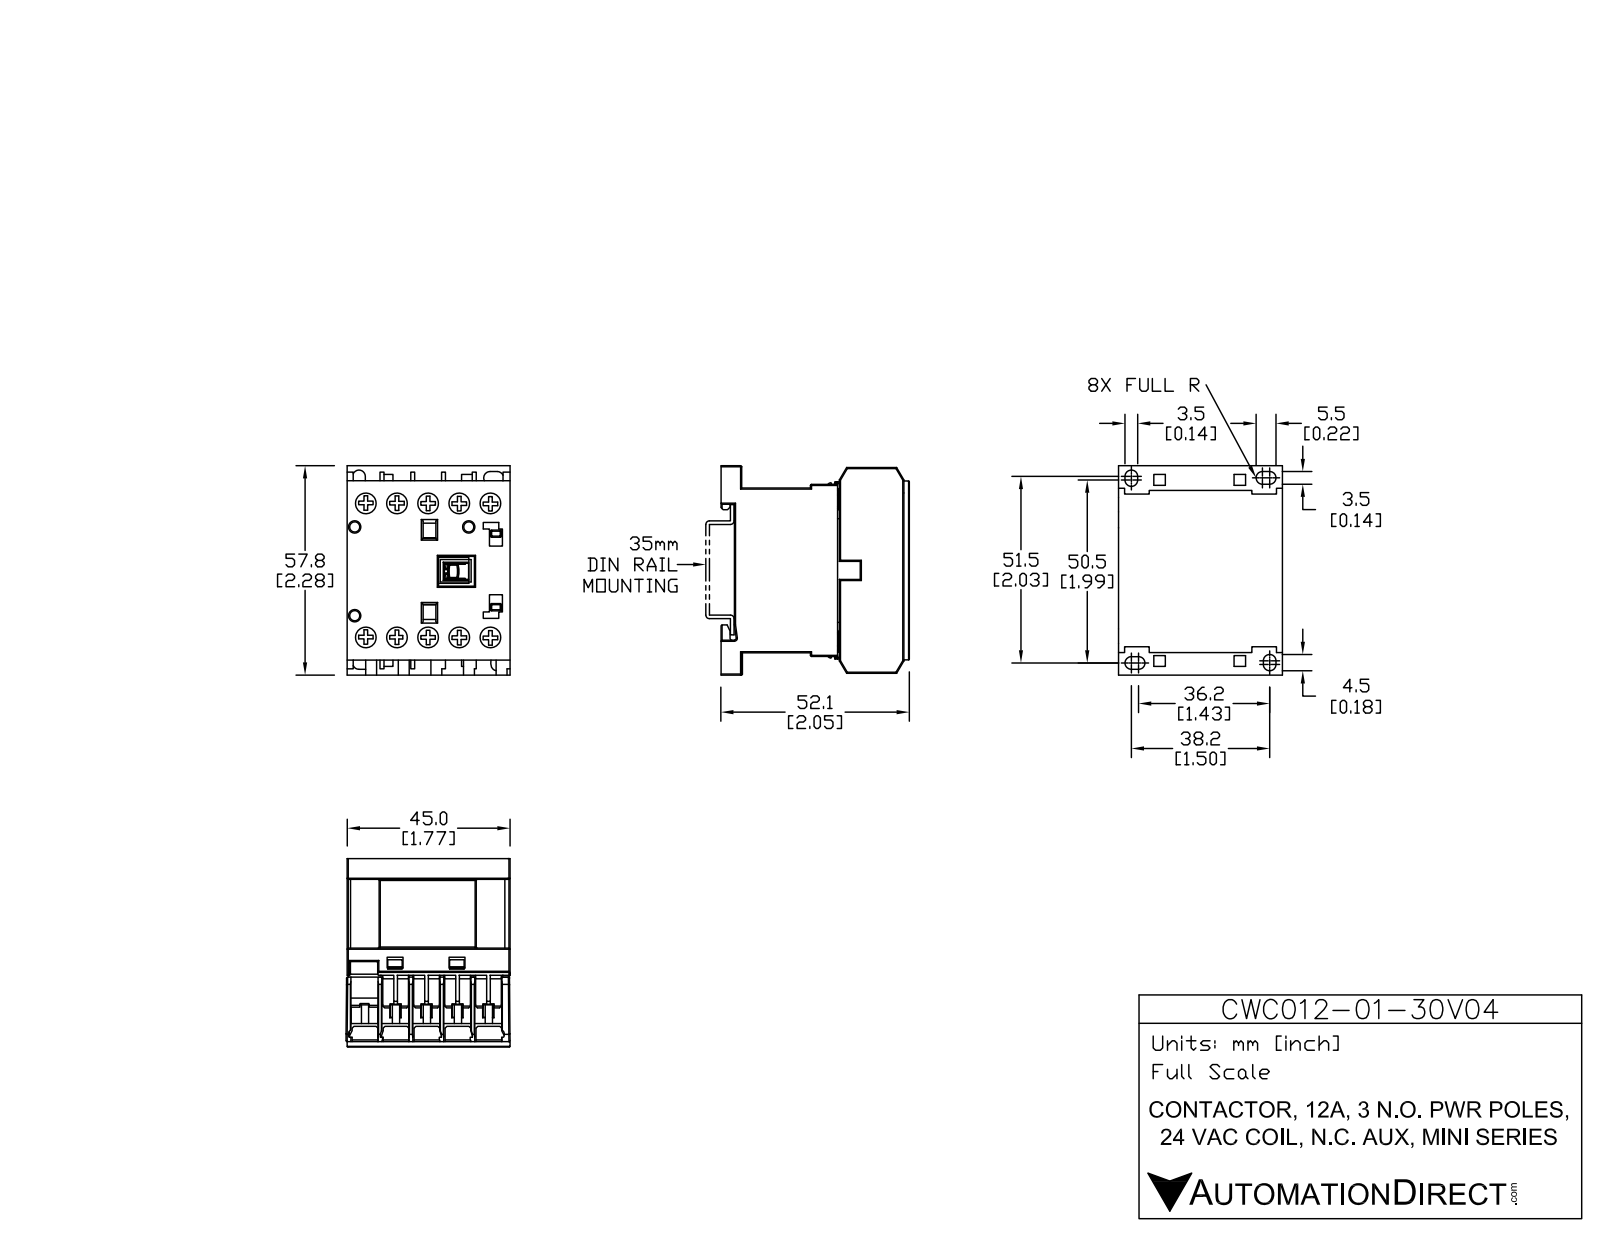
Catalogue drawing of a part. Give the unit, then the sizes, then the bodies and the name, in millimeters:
Units: millimetres
Overall size (bounding box): 58.04 × 52.12 × 45.75
Round holes (diameter × count): ⌀6.2 ×10, ⌀2.8 ×3
Round bosses / shafts (diameter × count): ⌀5.9 ×10
Partial cylindrical surfaces — rounded edges, fillets, slot ends (radius × count): R0.3 ×20, R1.72 ×6, R1.73 ×2, R0.32 ×1, R0.42 ×1, R0.55 ×1
Main face-to-face distances: 8.25, 45.5, 1.25, 16.5, 9.5, 5.5, 17.75, 5.13, 10.63, 7
Hole centre spacings: 8.55, 37.94, 17.1, 40.72, 36.96, 25.65, 44.99, 6.91
Volume: 97 133 mm³ · Surface area: 30 437 mm²
Bodies: 15 solids, 535 faces (445 planar, 90 cylindrical, 0 other)
Part name (STEP PRODUCT): CWC12-01-30V04
STEP written by: SolidWorks 2013 (AUTOMOTIVE_DESIGN)
